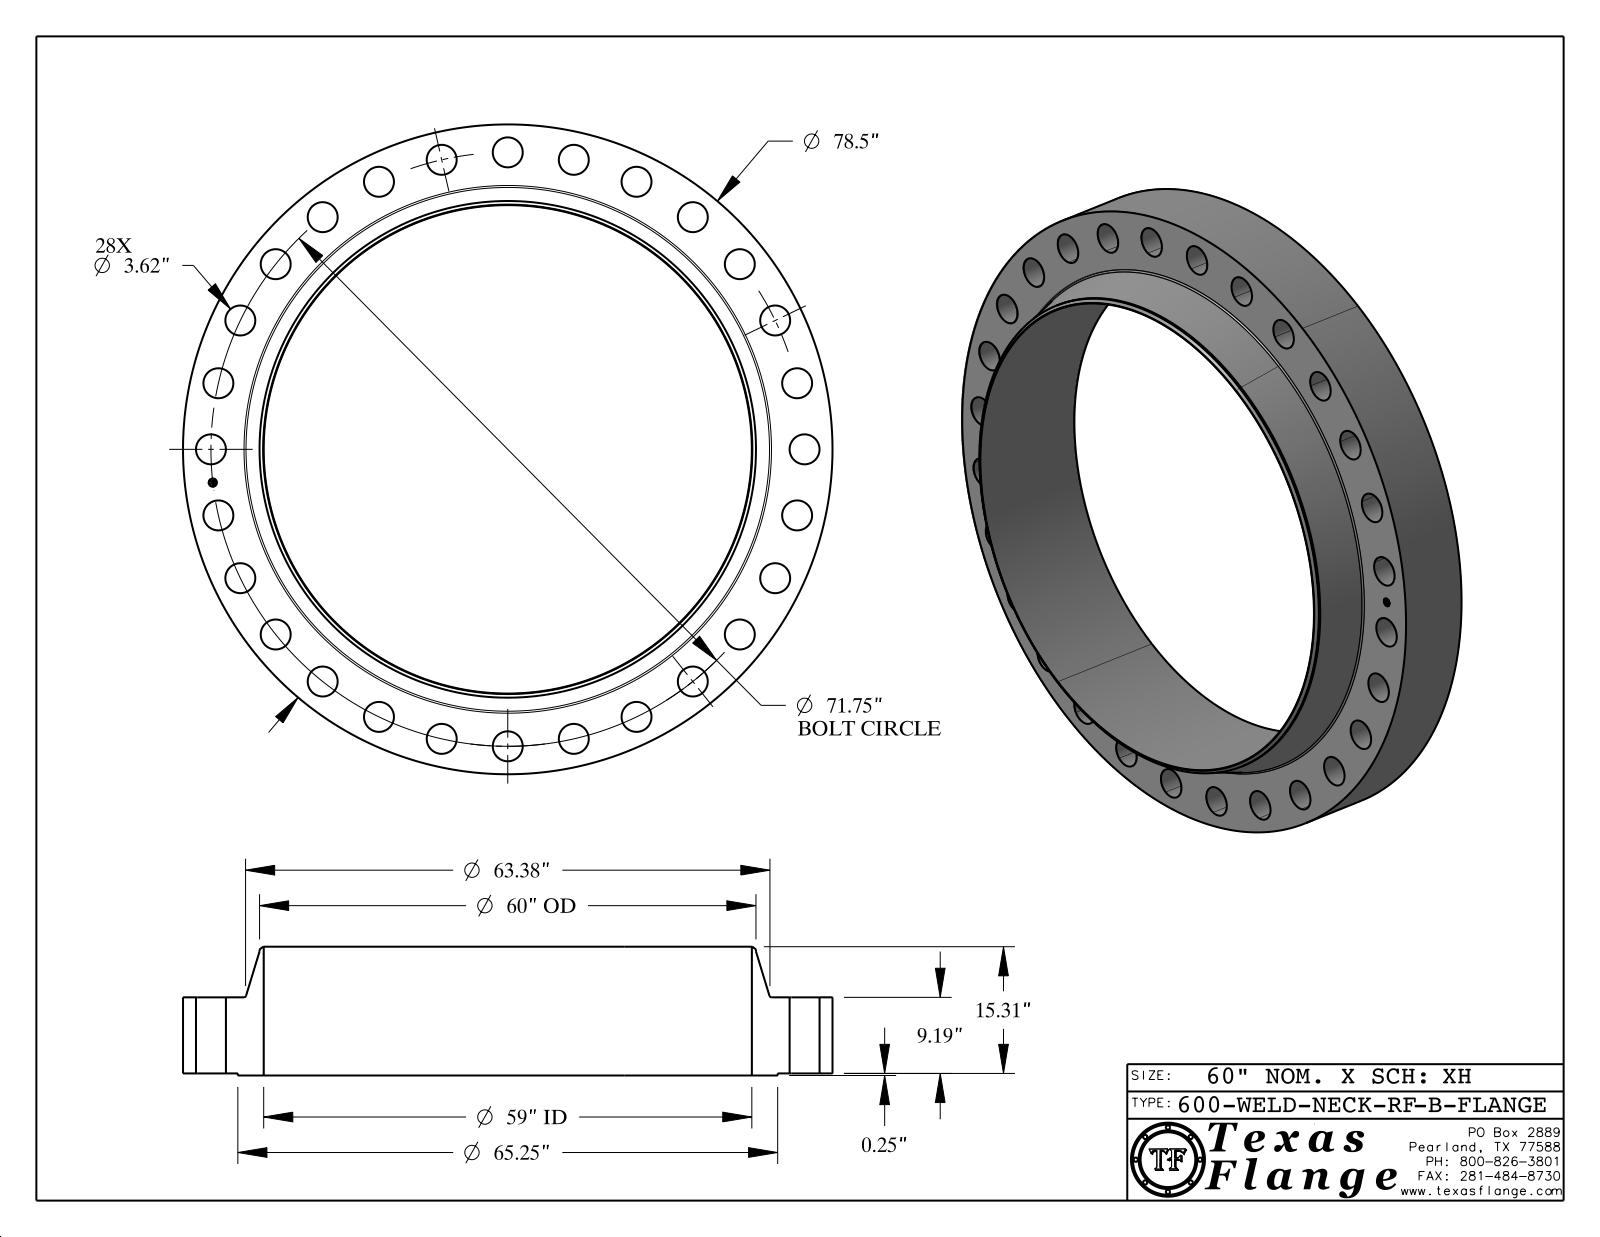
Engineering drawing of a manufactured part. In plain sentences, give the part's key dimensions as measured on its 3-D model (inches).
The part is named "600-WELD-NECK-RF, Series B". Its 3-D file was written by "CATIA V5 STEP AP214 (AUTOMOTIVE_DESIGN)". It is 1 solid with 459 faces: 369 planar, 84 cylindrical and 6 other. Overall it measures 78.5 by 78.5 by 15.56 inches. Its volume is 18 317 cubic inches and its surface area 12 616 square inches. Round holes: 28 of diameter 3.62, 1 of diameter 1, 1 of diameter 59. Round bosses or shafts: 8 of diameter 0.061, 1 of diameter 78.5, 1 of diameter 65.25, 1 of diameter 60, 1 of diameter 0.788. The main face-to-face distances are 9.19, 0.25, 9.44, 15.56, 15.31, 6.12, 9.425, 9.175, 0.015, 6.135. The hole center spacings are 44.735, 8.033, 35.875, 23.698, 69.951, 15.966, 31.131, 38.174.
